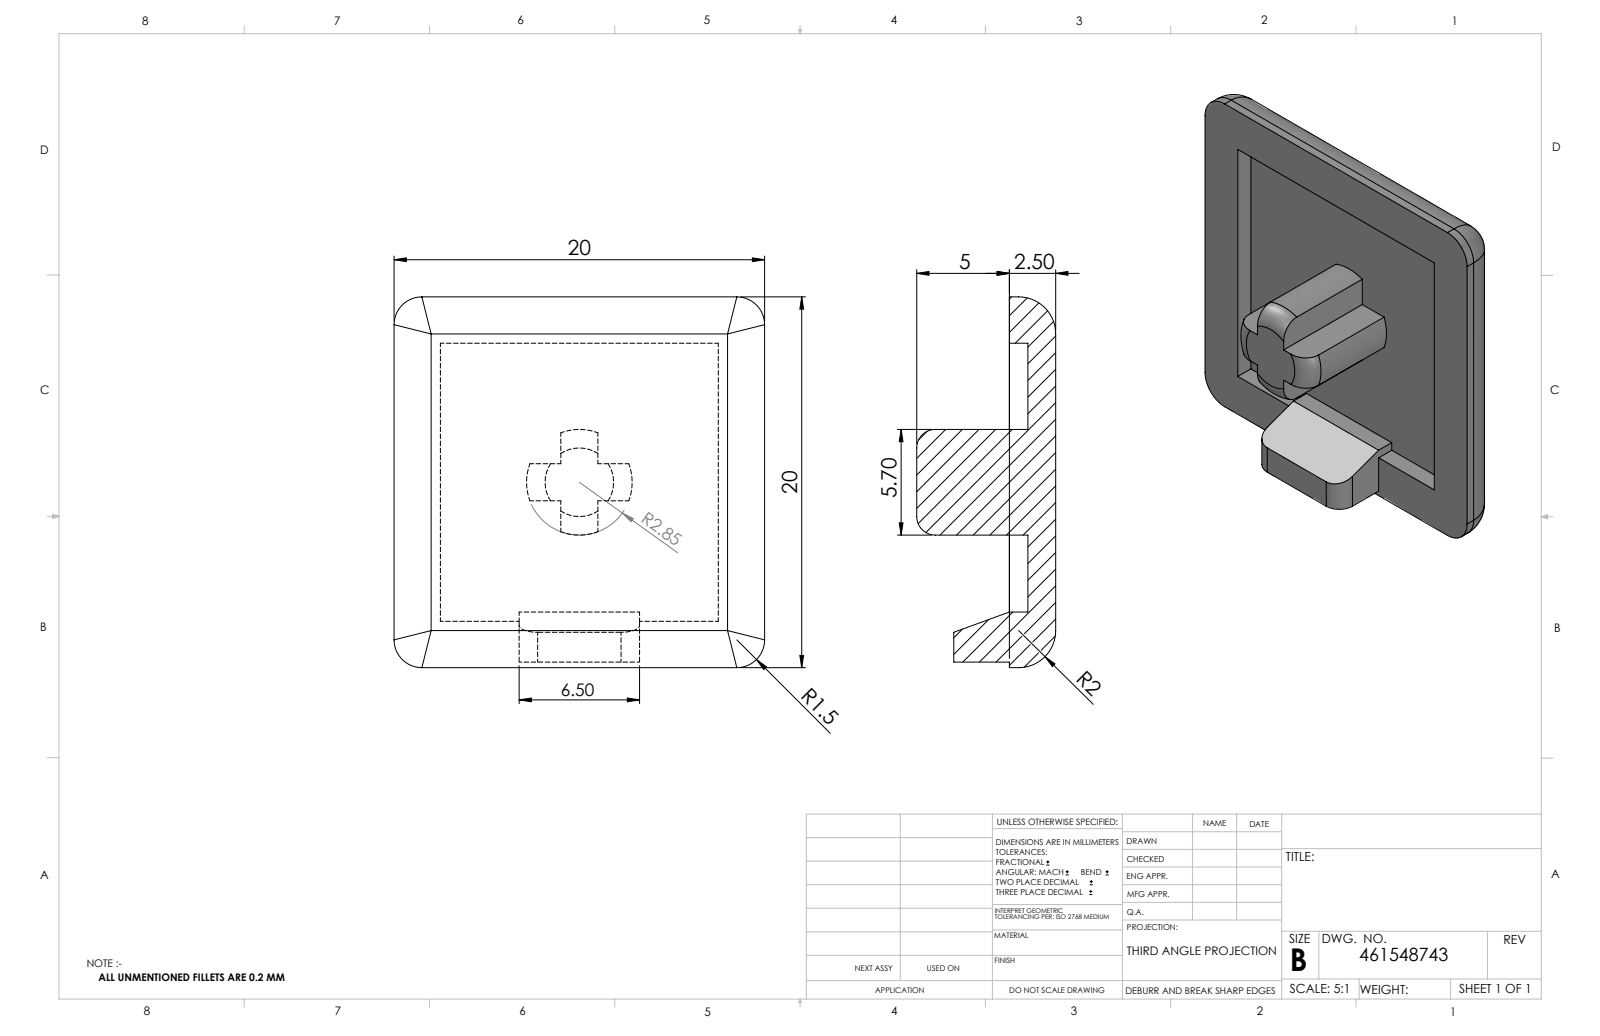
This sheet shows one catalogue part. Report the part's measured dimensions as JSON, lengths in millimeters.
{"part_name": "461548743", "step_written_by": "SolidWorks 2014 (CONFIG_CONTROL_DESIGN)", "units": "millimeters", "bodies": {"solids": 1, "faces": 52, "planar": 27, "cylindrical": 15, "other": 10}, "overall_size": [20, 20, 7.5], "volume_mm3": 859, "surface_area_mm2": 1150, "partial_cylinders_radius": [[1.5, 4], [2, 4], [1, 2], [2.85, 1]], "face_to_face_distances": [1.5, 2.5, 1, 6.5, 8.5, 2, 9, 11, 17.5, 15]}
